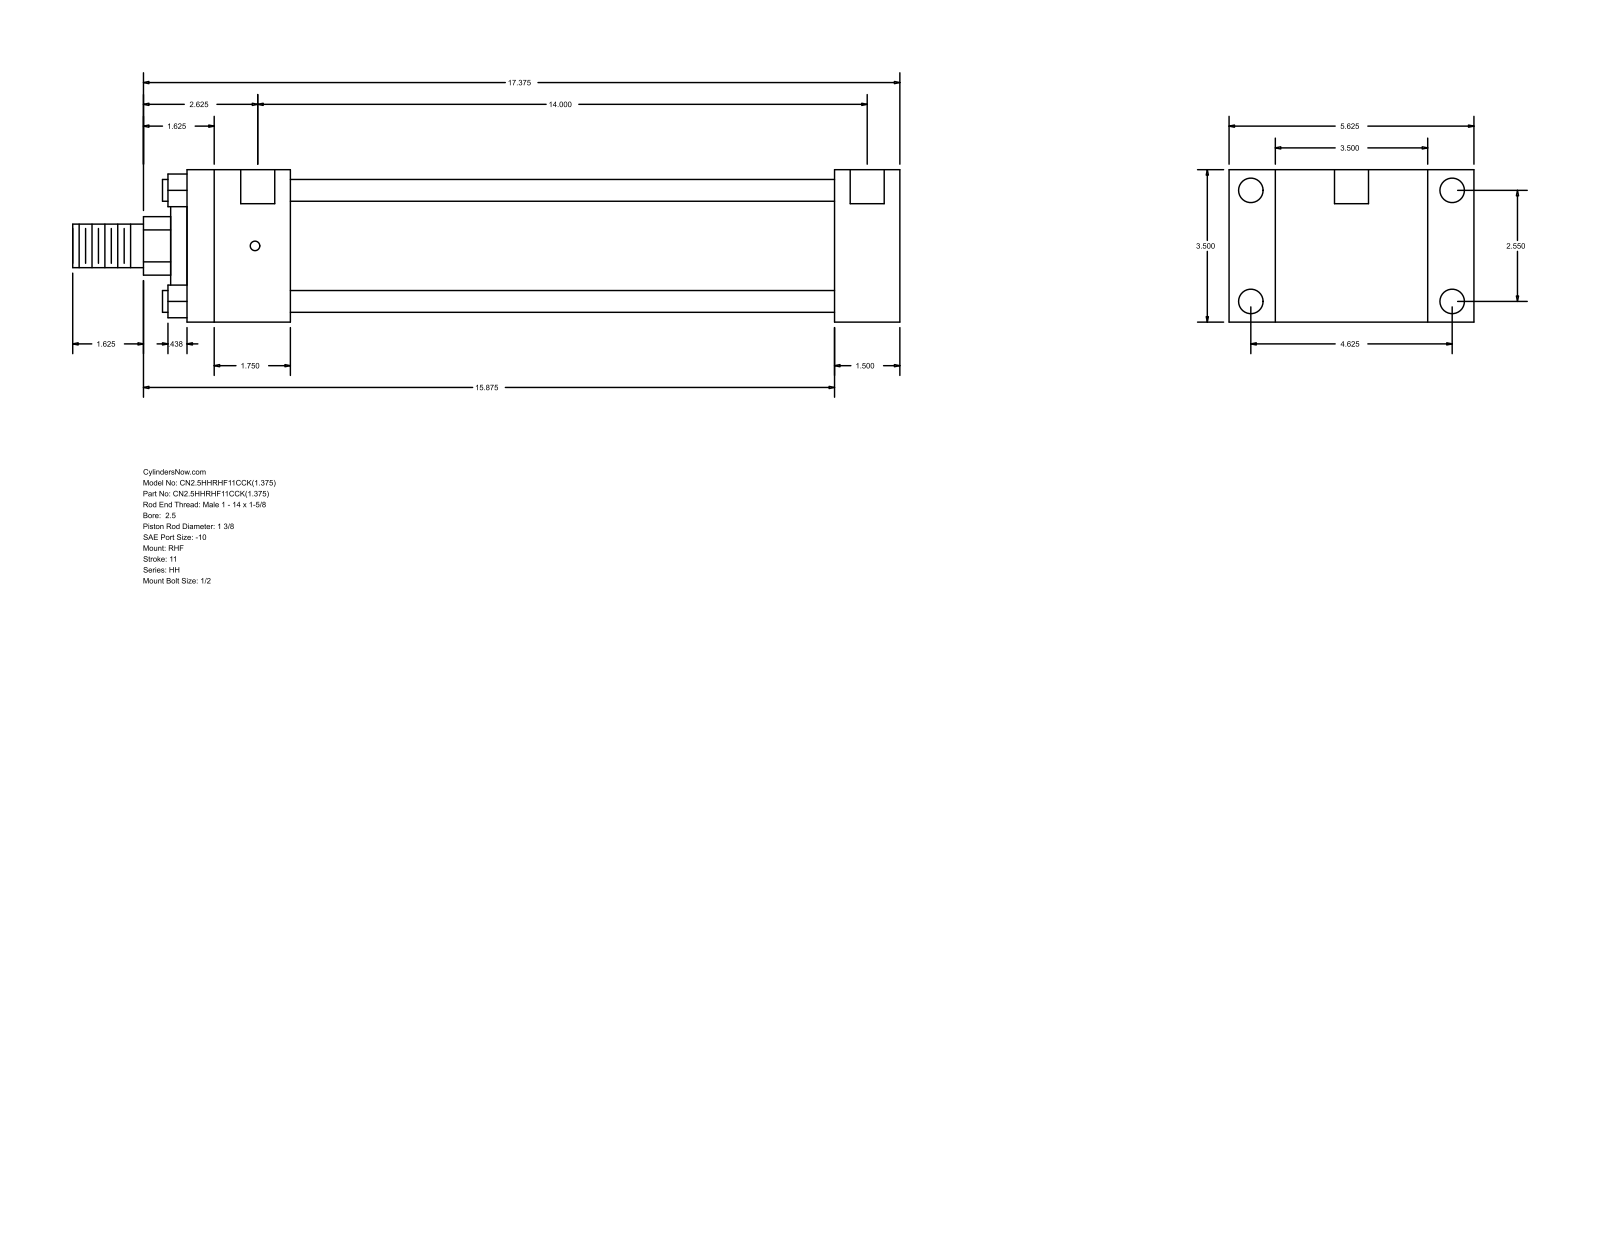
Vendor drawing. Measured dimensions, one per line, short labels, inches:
name: HH_RHF__0250_1.375
written by: GSSL Pune (CONFIG_CONTROL_DESIGN)
unit: in
bodies: 0 solids, 88 faces (60 planar, 28 cylindrical, 0 other)
size: 19 × 5.625 × 3.5
holes: 4× ⌀0.219, 4× ⌀0.563, 2× ⌀0.781
bosses: 4× ⌀0.5, 1× ⌀2.875, 1× ⌀2, 1× ⌀1.375, 1× ⌀1
rounds: 1× R0.672
face distances: 3.5, 1.5, 1.063, 4.563, 14.875, 16.375, 5.625, 2.375, 12.5, 14
hole spacings: 2.55, 4.625, 5.281, 14.125, 0.062, 0.063, 14, 14.062
